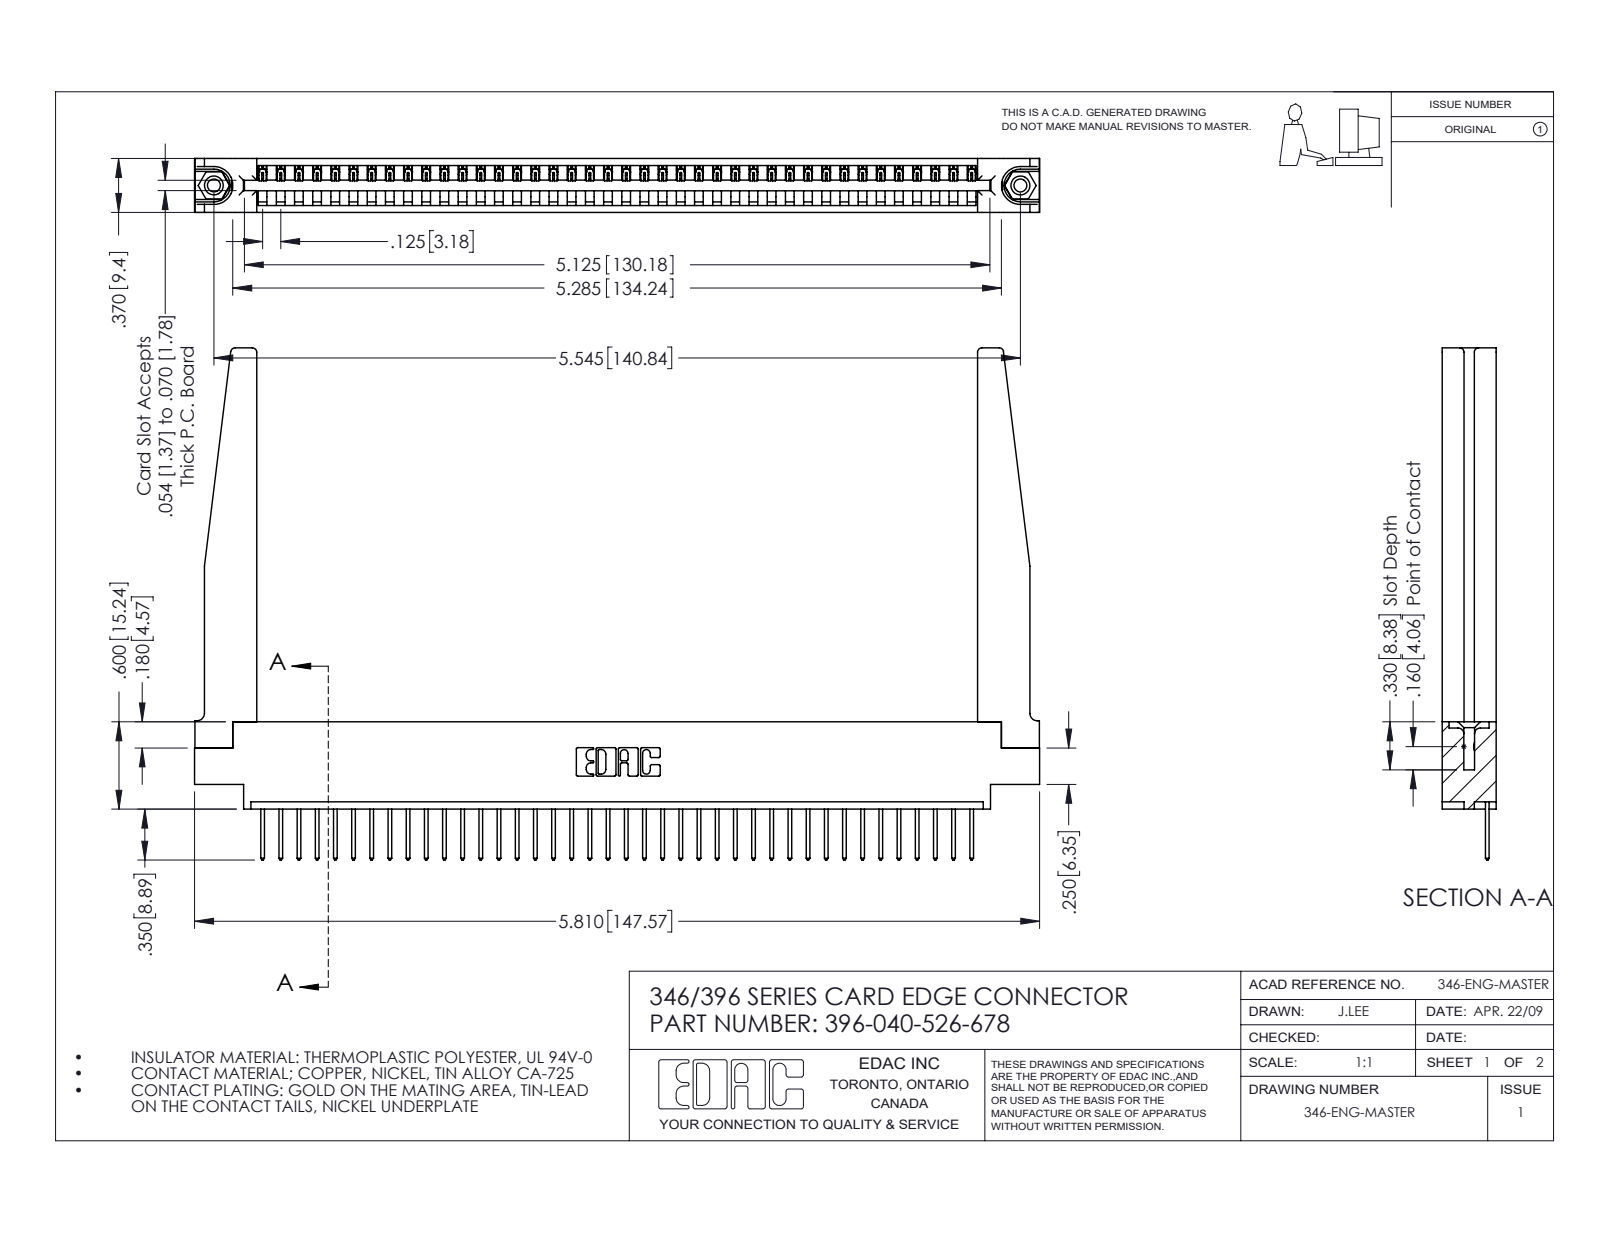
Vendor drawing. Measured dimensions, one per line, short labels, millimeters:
name: 346-220-078_345-220-078; 345-250-001_345-250-001-102; 396-040-526-678; 346 Part_0.170 Offset - 0.156 Dia-TH (+1 more)
written by: SolidWorks 2016 (CONFIG_CONTROL_DESIGN)
unit: mm
bodies: 45 solids, 2680 faces (1822 planar, 806 cylindrical, 52 other)
size: 147.6 × 89.4 × 9.4
volume: 20 830 mm³; area: 24 050 mm²
holes: 2× ⌀2.3, 2× ⌀3.2, 2× ⌀4, 1× ⌀1.6
bosses: 2× ⌀3.9
rounds: 80× R0.2, 80× R0.3, 22× R0.3, 8× R0.8, 6× R0.2, 6× R0.8, 3× R0.7, 2× R0.8
face distances: 9.4, 1.2, 8.2, 1.8, 3.8, 6.4, 3.8, 7.6, 0.6, 5.6
hole spacings: 6.2, 135.5, 140.8
